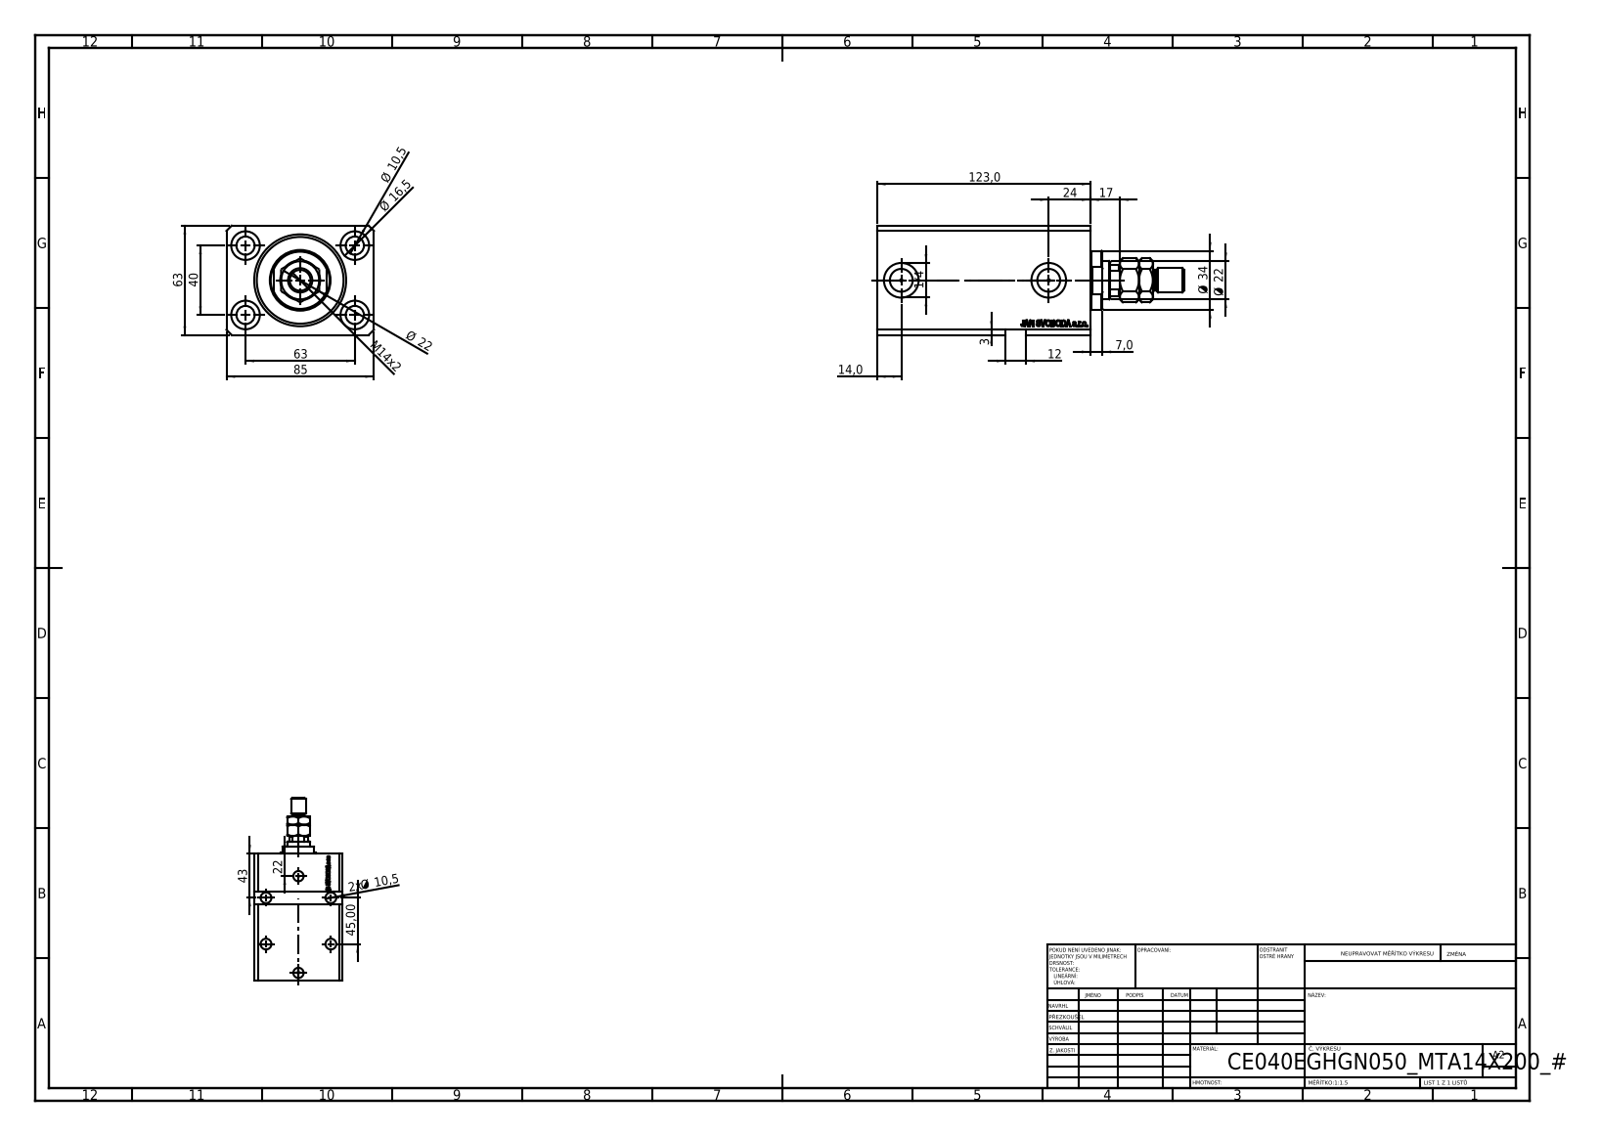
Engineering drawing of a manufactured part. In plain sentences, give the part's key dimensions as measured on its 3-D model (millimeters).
The part is named "V250CE_VC_E; MTA; V250CE_C_VCP; V250CE_E_Body". Its 3-D file was written by "SolidWorks 2019 (CONFIG_CONTROL_DESIGN)". It is 4 solids with 986 faces: 474 planar, 108 cylindrical and 404 other. Overall it measures 177 by 85 by 63 millimeters. Its volume is 553 313 cubic millimeters and its surface area 110 806 square millimeters. Round holes: 8 of diameter 10.5, 4 of diameter 1.25, 4 of diameter 16.5, 2 of diameter 10, 2 of diameter 13.16, 2 of diameter 20, 1 of diameter 12.5, 1 of diameter 22, 1 of diameter 40, 1 of diameter 53. Round bosses or shafts: 1 of diameter 34, 1 of diameter 14, 1 of diameter 12. Partial cylindrical surfaces (rounded edges, fillets, slot ends): 1 of radius 10.5. The main face-to-face distances are 63, 85, 17, 123, 106, 11.4, 94.6, 111.6, 56, 11. The hole center spacings are 37.31, 63, 37.86, 40, 41.8, 42.15, 45, 73.13.
